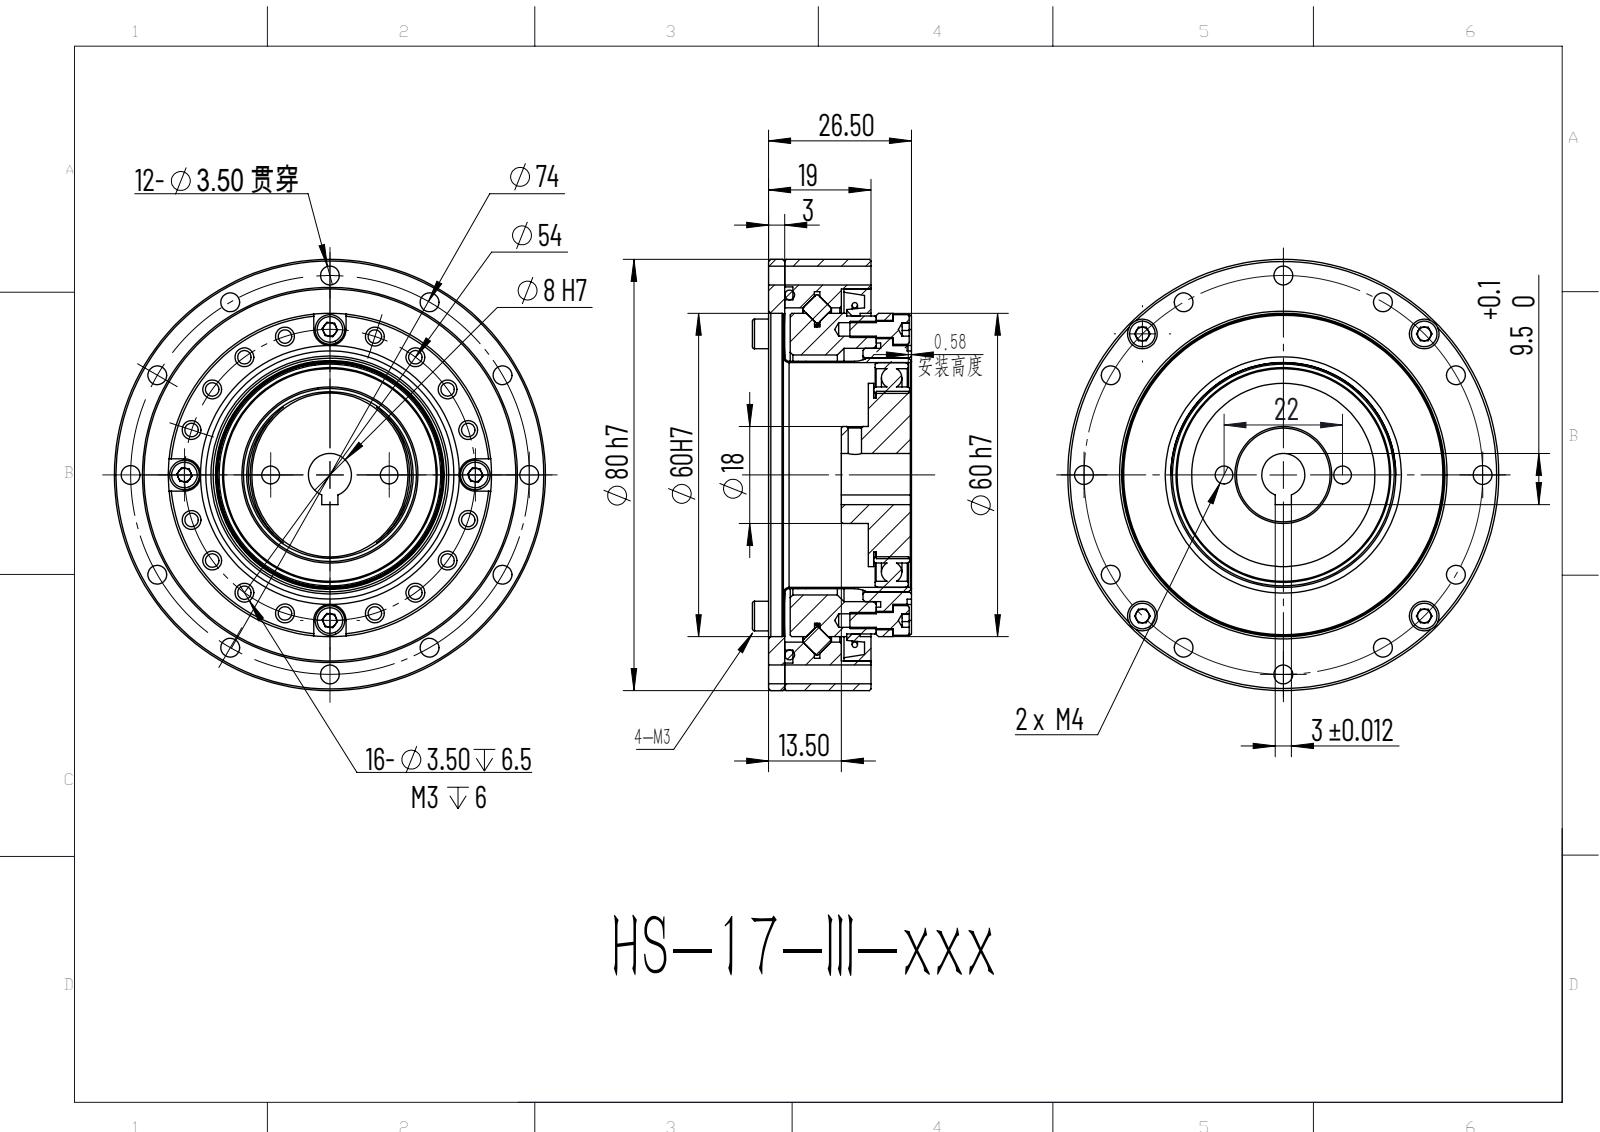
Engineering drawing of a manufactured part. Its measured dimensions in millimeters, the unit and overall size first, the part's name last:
Units: millimetres
Overall size (bounding box): 80 × 80 × 29.5
Round holes (diameter × count): ⌀3.5 ×32, ⌀2.5 ×24, ⌀3.4 ×4, ⌀3.3 ×2, ⌀1.6 ×1, ⌀2.4 ×1, ⌀4.3 ×1, ⌀8 ×1, ⌀30.3 ×1, ⌀39.44 ×1, ⌀41.72 ×1, ⌀43.34 ×1
Round bosses / shafts (diameter × count): ⌀4 ×36, ⌀5.5 ×8, ⌀3 ×8, ⌀80 ×1, ⌀65 ×1, ⌀60 ×1, ⌀55 ×1, ⌀46.04 ×1
Partial cylindrical surfaces — rounded edges, fillets, slot ends (radius × count): R2.02 ×36, R3 ×4
Main face-to-face distances: 1, 16, 3, 4, 19, 17, 0.5, 6.5, 20, 15.5
Hole centre spacings: 27, 38.18, 48.11, 16.69, 24.51, 37, 51.35, 8.44
Volume: 71 424 mm³ · Surface area: 65 672 mm²
Bodies: 91 solids, 995 faces (559 planar, 251 cylindrical, 185 other)
Part name (STEP PRODUCT): HS-17-III; hexagon socket head cap screws gb_GB_FASTENER_SCREWS_HSHCS M3X8-C; ??????-STXB-17050; ???????-STXB-17050 (+8 more)
STEP written by: ONSHAPE BY PTC INC, 1.201 (AP242_MANAGED_MODEL_BASED_3D_ENGINEERING_MIM_LF)
